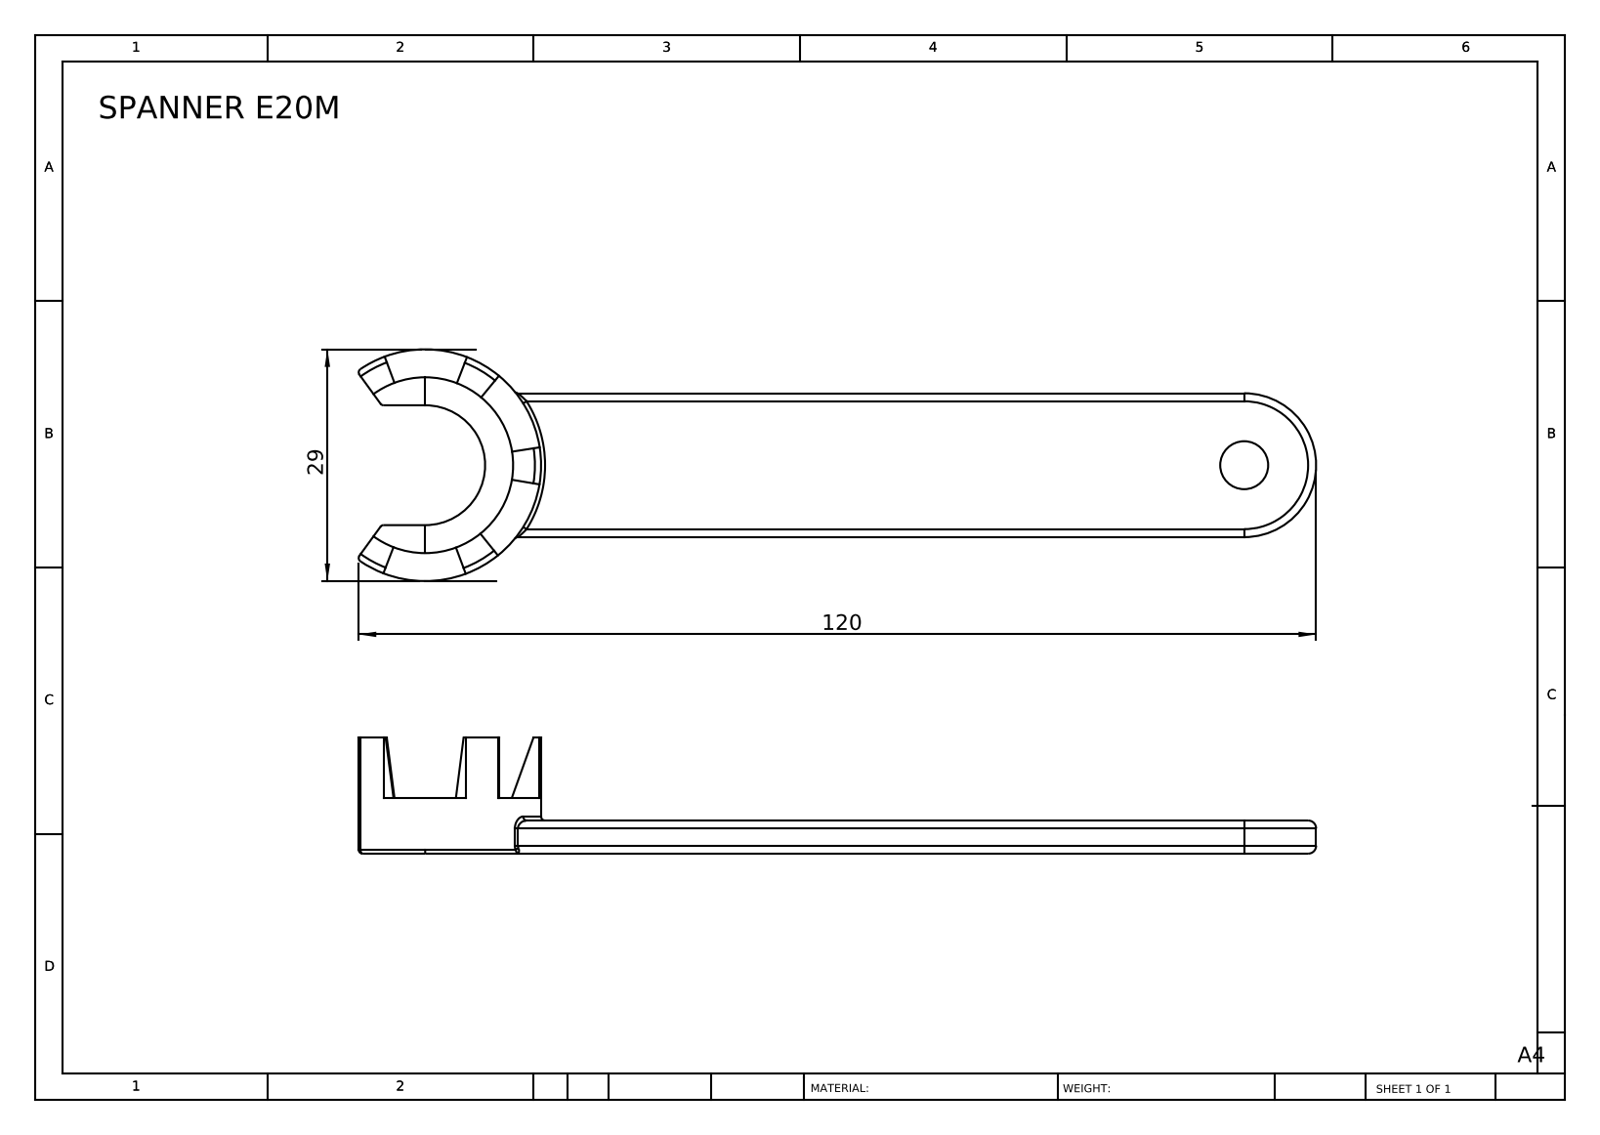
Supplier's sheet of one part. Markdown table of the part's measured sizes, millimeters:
| quantity | value |
| --- | --- |
| part name | SPANNER E20M |
| STEP written by | SolidWorks 2014 (CONFIG_CONTROL_DESIGN) |
| units | millimeters |
| bodies | 1 solid, 67 faces (25 planar, 19 cylindrical, 23 other) |
| overall size | 119.8 × 29 × 14.5 |
| volume | 9 303 mm³ |
| surface area | 5 850 mm² |
| round holes (diameter × count) | 6 × 1 |
| partial cylindrical surfaces (radius × count) | 0.5 × 8, 1 × 4, 7.5 × 1, 9 × 1, 14.5 × 1 |
| main face-to-face distances | 4.15, 18, 2.85, 7, 1.5, 16.5, 7.5, 10.35, 14.5, 15 |
